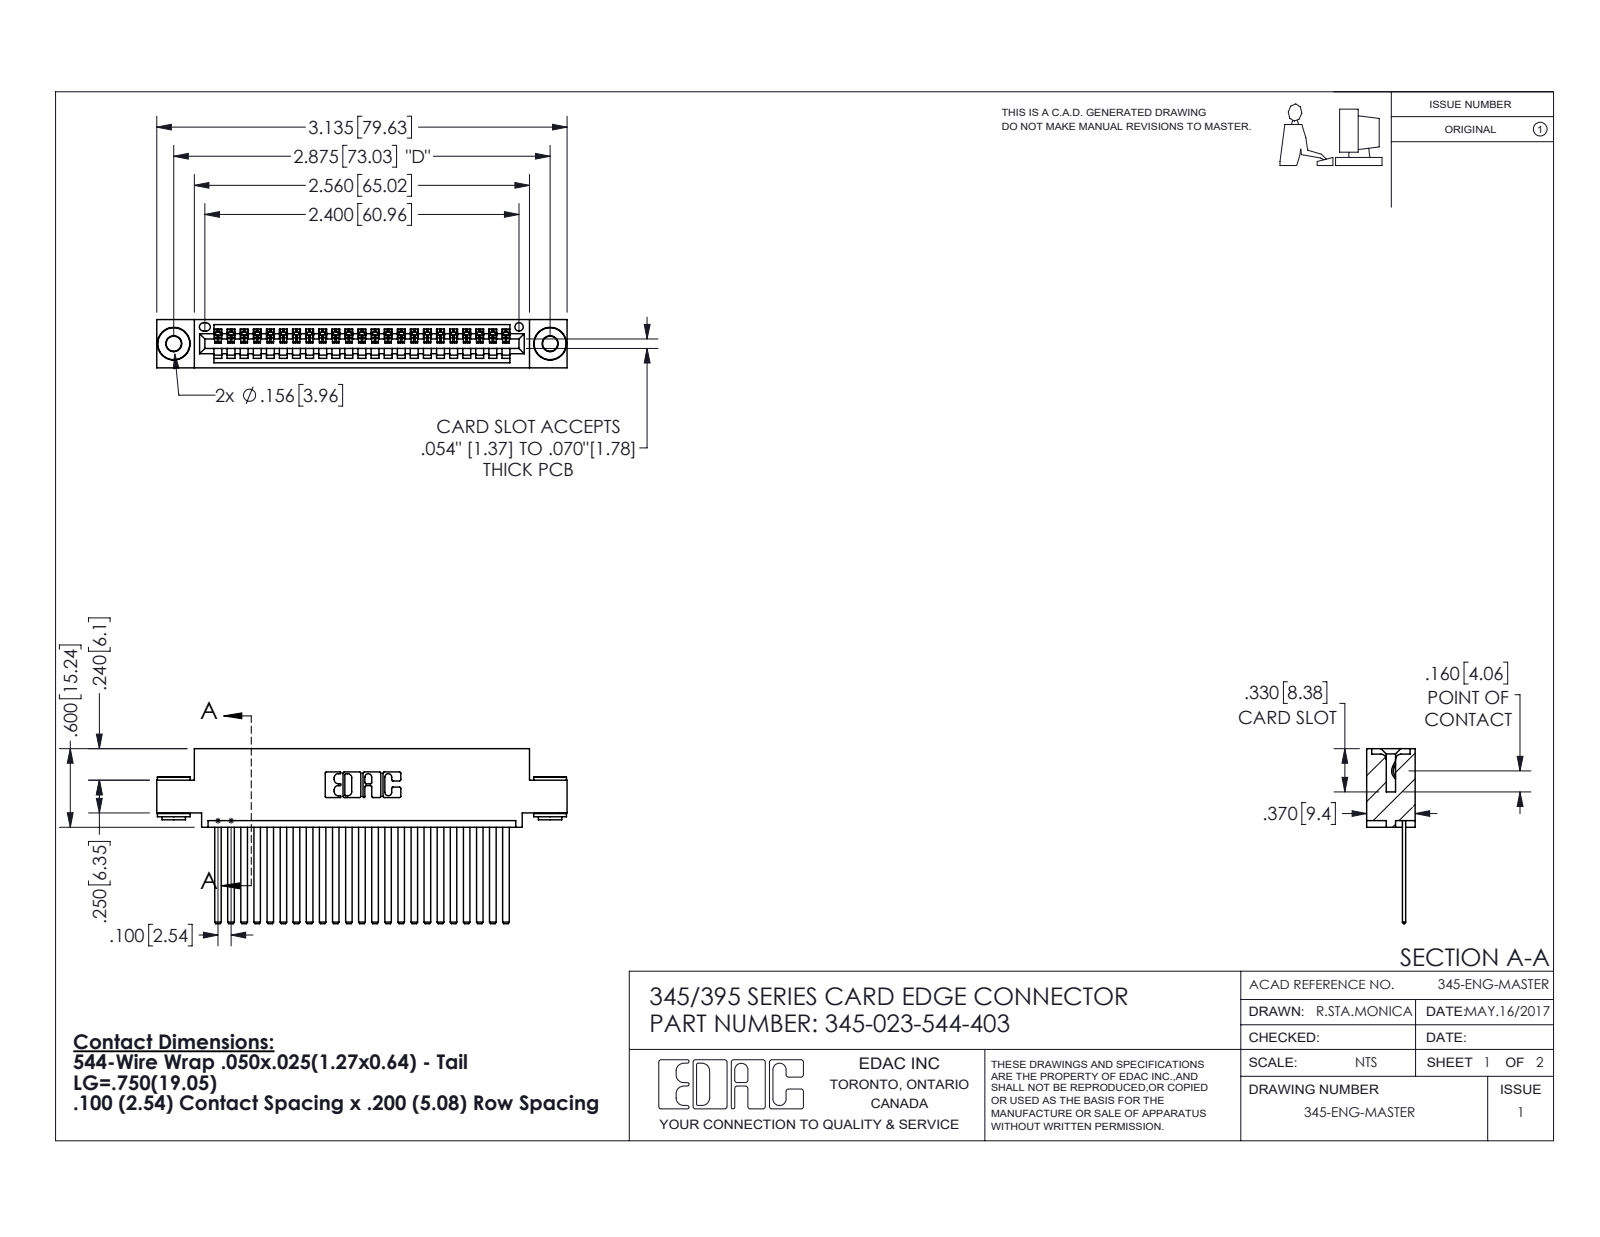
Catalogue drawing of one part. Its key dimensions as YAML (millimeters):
part_name: "345-023-544-403; 345-250-002_345-250-002-102; 345 Part_0.110 Offset - 0.156 Dia-TH; 345-292-001_345-293-144"
step_written_by: "SolidWorks 2016 (CONFIG_CONTROL_DESIGN)"
units: millimeters
bodies: {solids: 26, faces: 1364, planar: 922, cylindrical: 434, other: 8}
overall_size: [79.6, 34, 9.4]
volume: 7620
surface_area: 10960
round_holes:
  - {diameter: 2.9, count: 2}
  - {diameter: 4, count: 2}
  - {diameter: 1.6, count: 1}
round_bosses_or_shafts:
  - {diameter: 6.4, count: 2}
  - {diameter: 4.6, count: 2}
  - {diameter: 3.5, count: 2}
partial_cylinders:
  - {radius: 0.2, count: 46}
  - {radius: 0.3, count: 22}
  - {radius: 0.2, count: 6}
  - {radius: 0.8, count: 6}
  - {radius: 0.7, count: 3}
  - {radius: 0.8, count: 2}
  - {radius: 1, count: 2}
  - {radius: 0.4, count: 1}
face_to_face_distances: [1.8, 7.6, 0.6, 2.5, 6.9, 9.4, 5.1, 5.7, 3.8, 1.8]
hole_center_spacings: [6.9, 67.1, 73]
